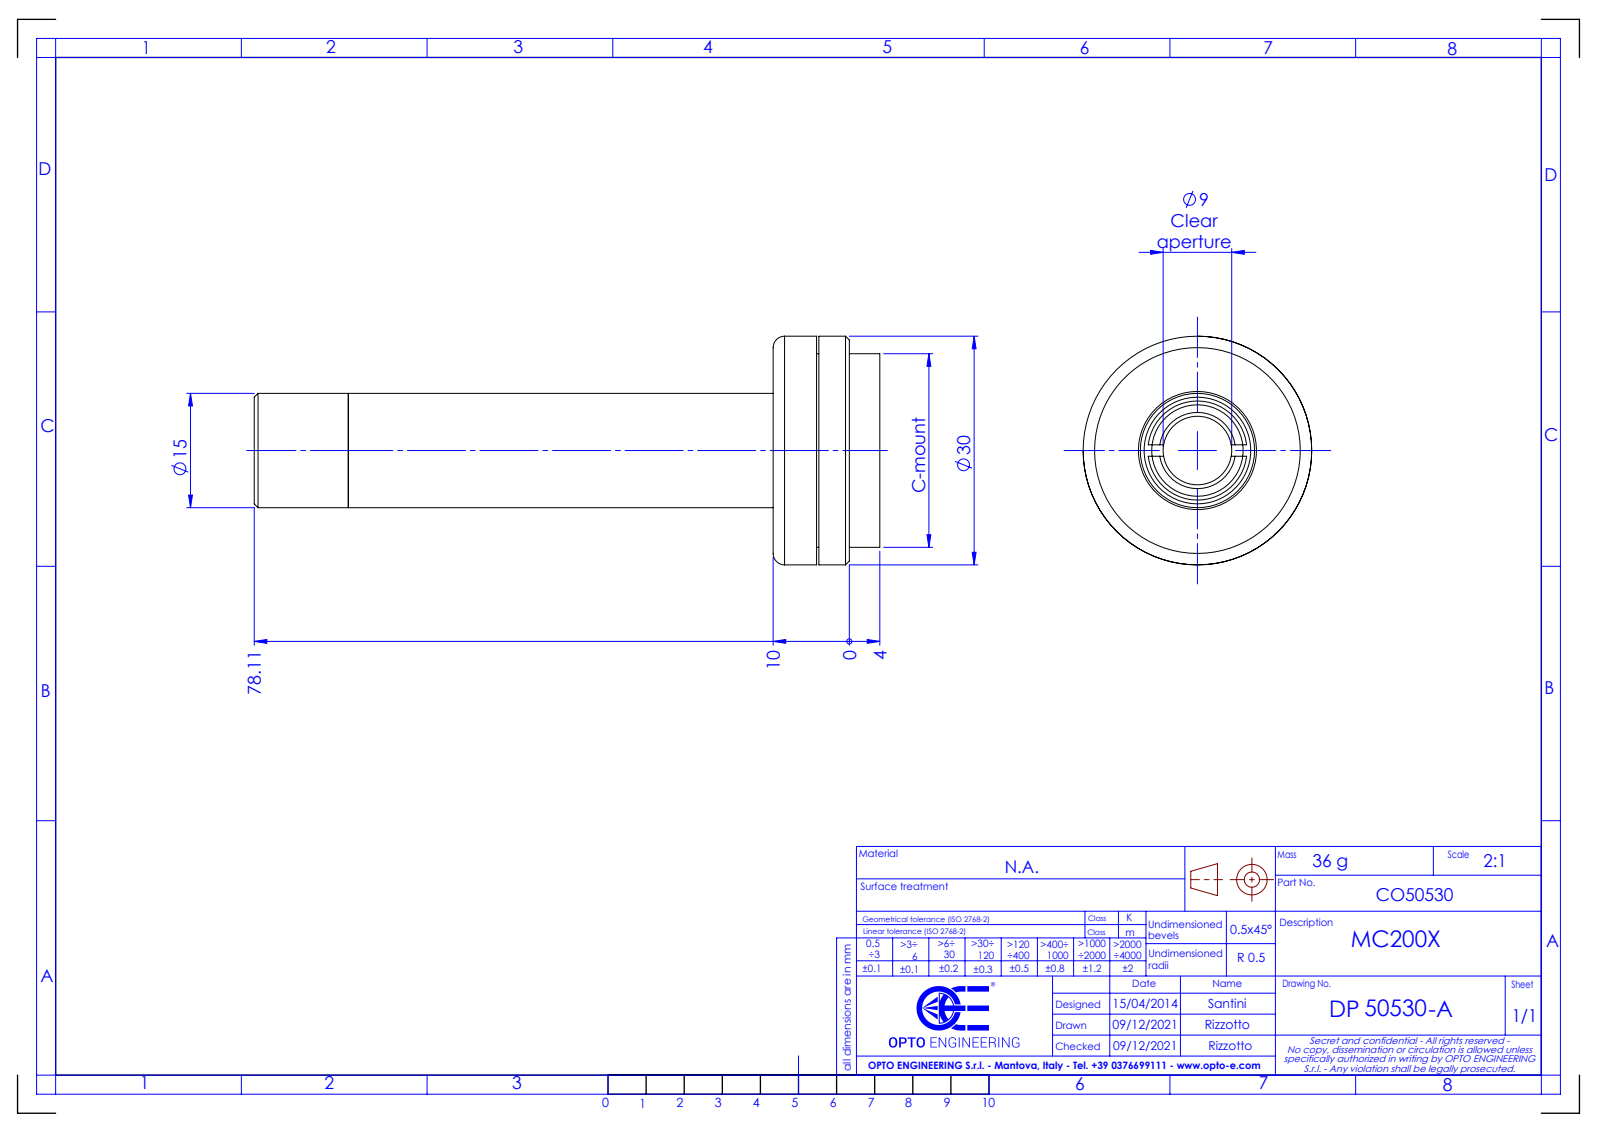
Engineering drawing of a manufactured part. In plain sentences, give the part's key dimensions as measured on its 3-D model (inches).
The part is named "DP50530-A_MC200X". Its 3-D file was written by "SolidWorks 2021 (CONFIG_CONTROL_DESIGN)". It is 0 solids with 49 faces: 16 planar, 18 cylindrical and 15 other. Overall it measures 3.233 by 1.181 by 1.181 inches. Round holes: 1 of diameter 0.354, 1 of diameter 0.472. Round bosses or shafts: 1 of diameter 1.181, 1 of diameter 1, 1 of diameter 0.591, 1 of diameter 0.571. The main face-to-face distances are 0.157, 0.236, 0.224, 0.394, 0.169, 0.551, 0.327, 0.315, 2.681, 2.906.
